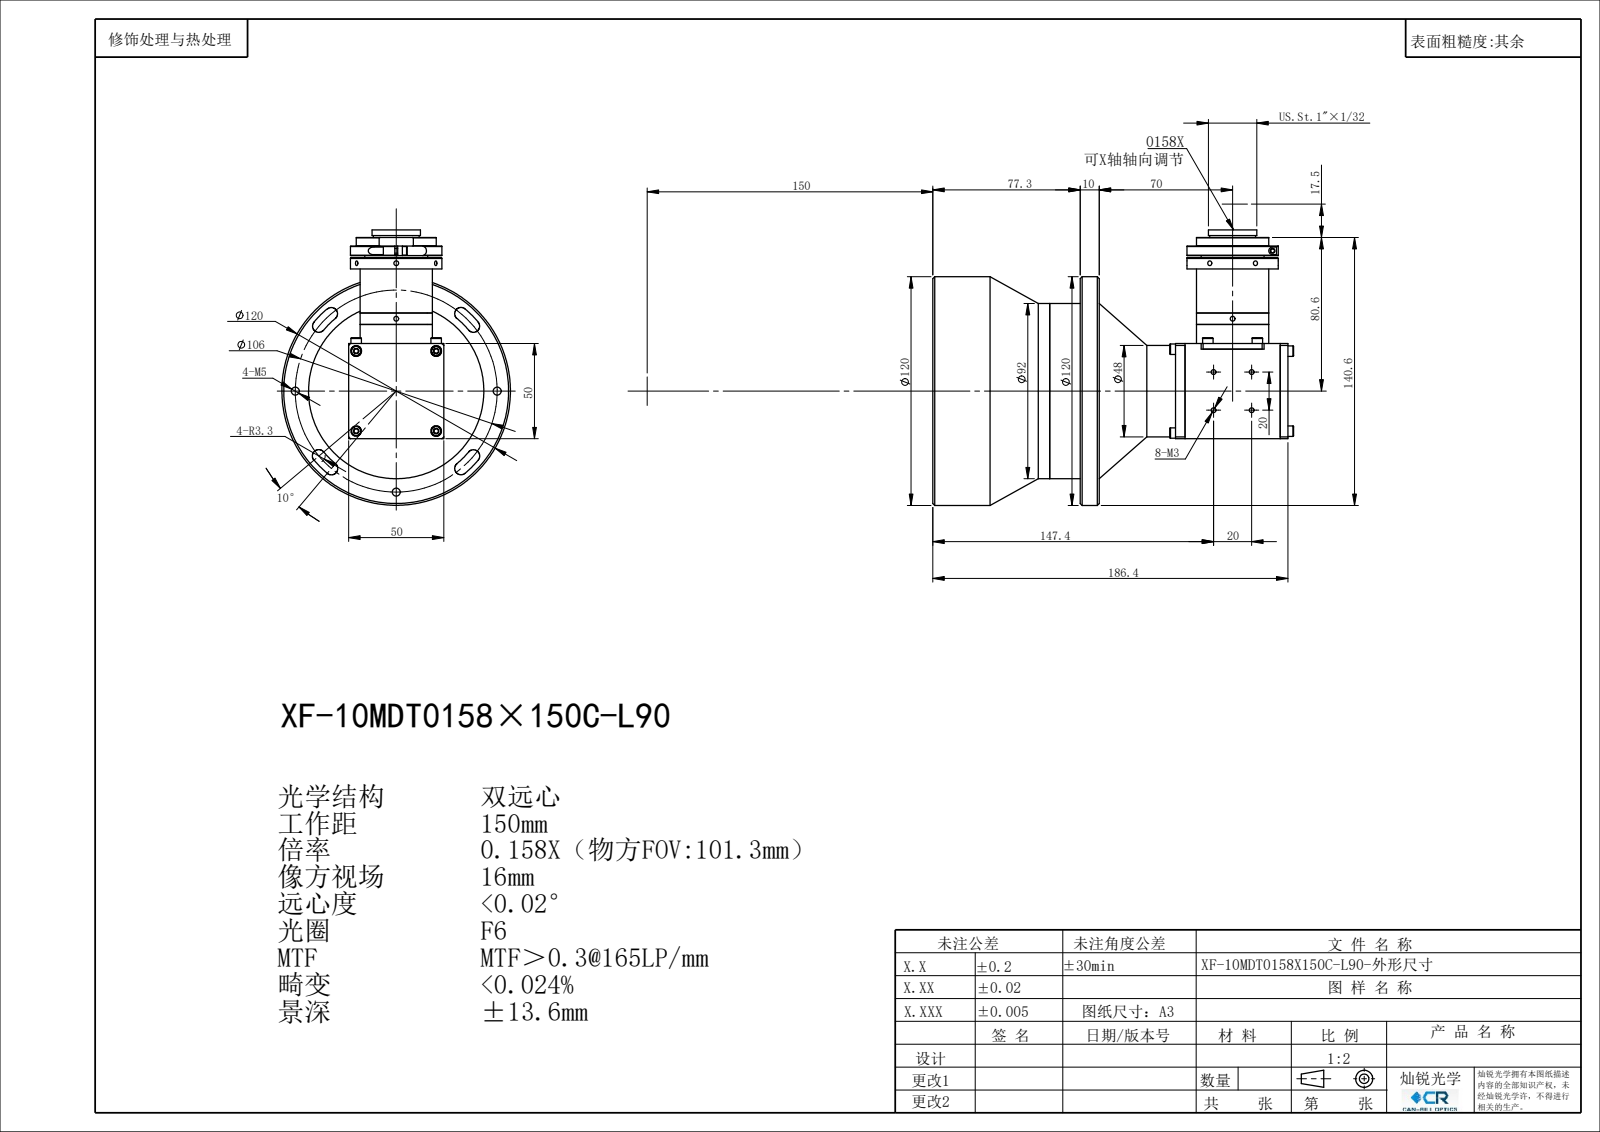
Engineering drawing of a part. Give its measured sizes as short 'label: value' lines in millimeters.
name: XF-10MDT0158X150C-L90
written by: SolidWorks 2018 (CONFIG_CONTROL_DESIGN)
unit: mm
bodies: 0 solids, 378 faces (162 planar, 136 cylindrical, 80 other)
size: 189.36 × 144.61 × 120
holes: 11× ⌀2.5, 4× ⌀4.2, 1× ⌀3, 1× ⌀22, 1× ⌀23, 1× ⌀25.4, 1× ⌀30, 1× ⌀111, 1× ⌀115
bosses: 12× ⌀5.5, 2× ⌀48, 1× ⌀120, 1× ⌀92, 1× ⌀38, 1× ⌀24, 1× ⌀4.5
rounds: 8× R3.3, 1× R2, 1× R3, 1× R6, 1× R18, 1× R21, 1× R49.7, 1× R56.3
face distances: 50, 10, 99.02, 109.02, 4, 105.02, 95.02, 6, 55.02, 45.02
hole spacings: 20, 21.21, 30, 53, 74.95, 28.28, 42.43, 85.51
